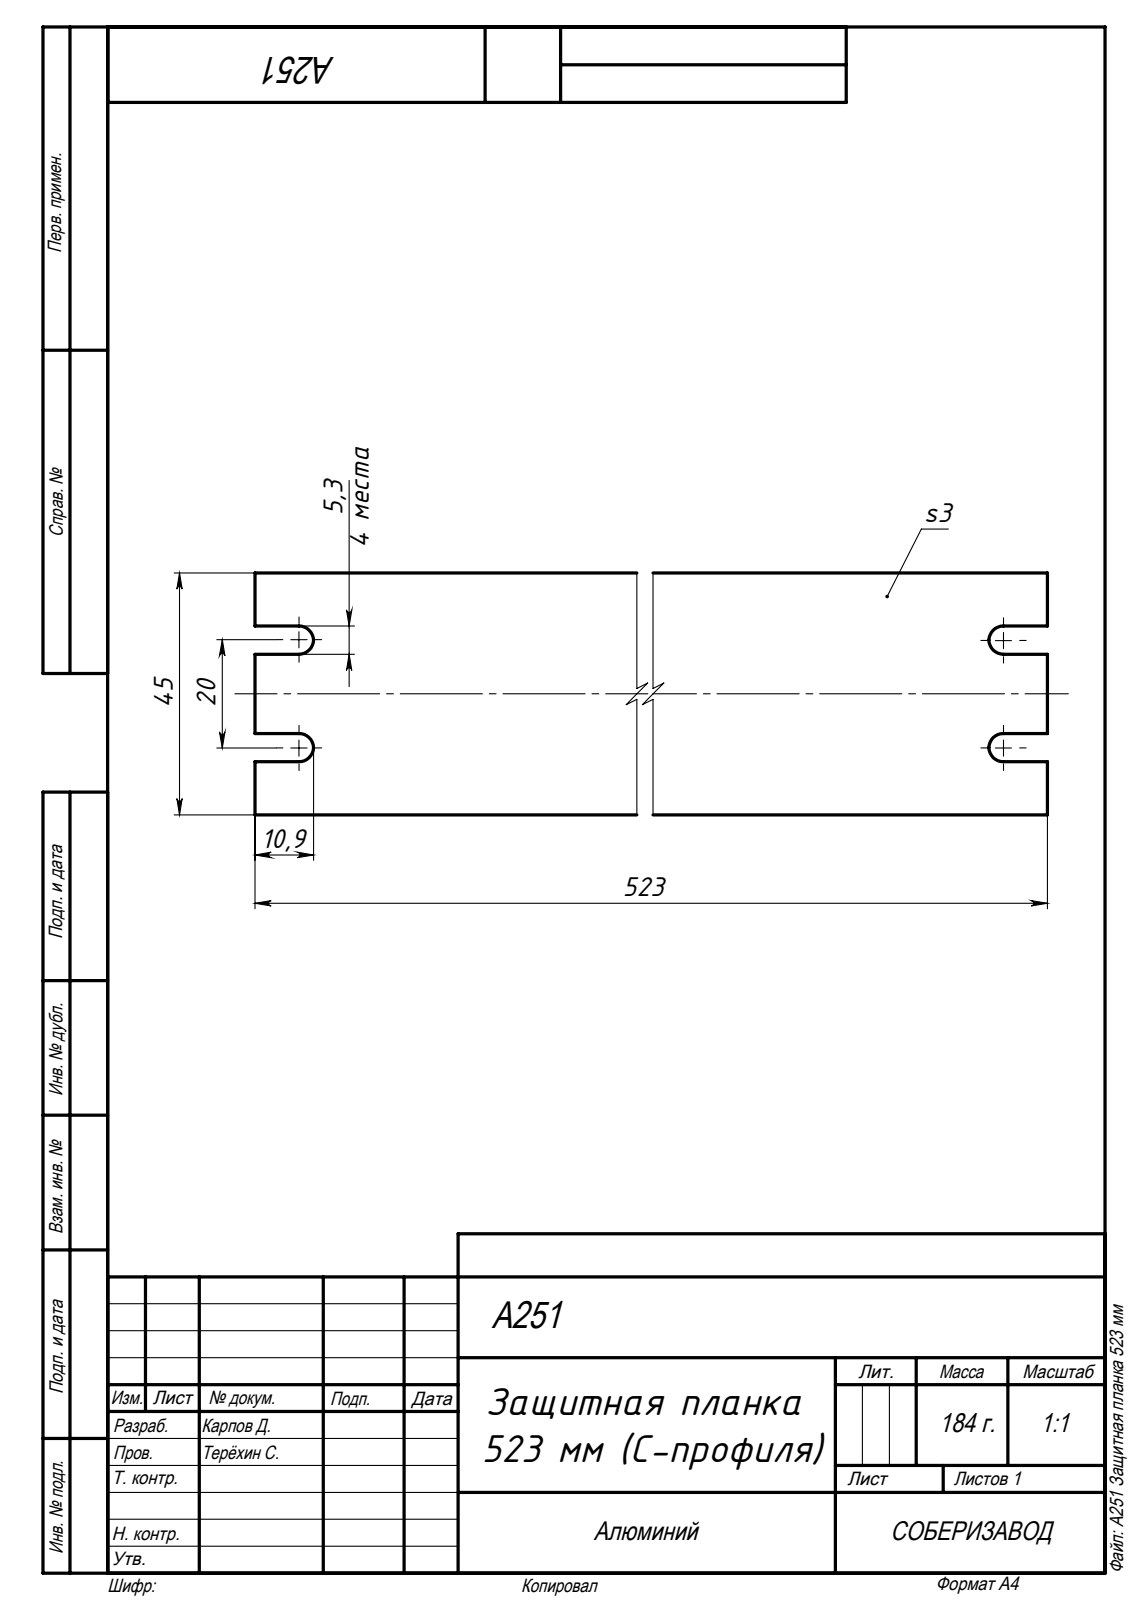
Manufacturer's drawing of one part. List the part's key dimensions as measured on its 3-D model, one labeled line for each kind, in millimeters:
Part name (STEP PRODUCT): A251 Защитная планка 523 мм
STEP written by: SolidWorks 2018 (AUTOMOTIVE_DESIGN)
Units: millimetres
Bodies: 1 solid, 26 faces (18 planar, 8 cylindrical, 0 other)
Overall size (bounding box): 523 × 44.9 × 3
Volume: 69 802 mm³ · Surface area: 50 175 mm²
Partial cylindrical surfaces — rounded edges, fillets, slot ends (radius × count): R2.7 ×8
Main face-to-face distances: 3, 44.9, 523, 9.85, 15.1, 29.8, 35.05, 5.25, 19.95, 25.2
